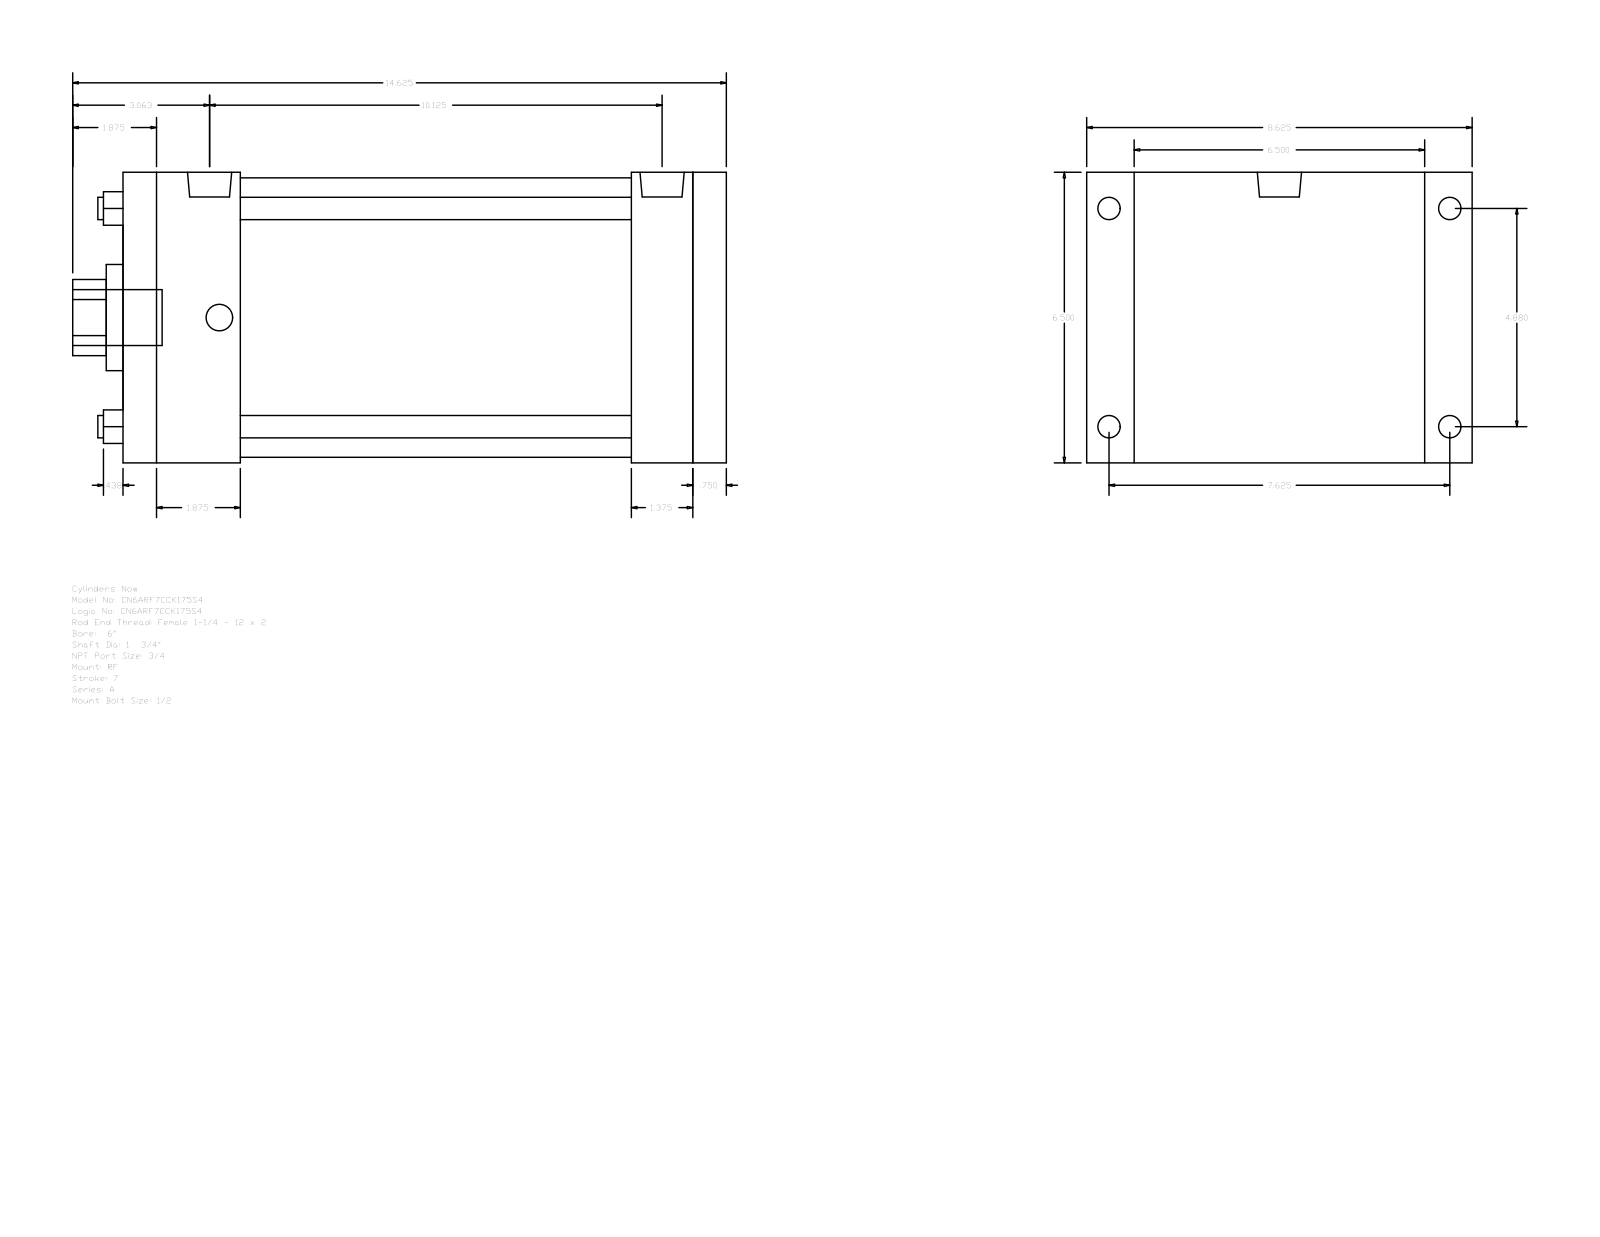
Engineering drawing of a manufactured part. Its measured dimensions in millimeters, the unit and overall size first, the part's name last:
Units: millimetres
Overall size (bounding box): 371.48 × 219.07 × 165.1
Round holes (diameter × count): ⌀12.7 ×4, ⌀44.45 ×1, ⌀60.33 ×1, ⌀158.75 ×1
Round bosses / shafts (diameter × count): ⌀15.08 ×4, ⌀12.7 ×4, ⌀25.12 ×2, ⌀31.75 ×1
Partial cylindrical surfaces — rounded edges, fillets, slot ends (radius × count): R21.63 ×1
Main face-to-face distances: 165.1, 342.91, 19.05, 323.86, 66.68, 257.18, 276.23, 288.93, 222.25, 34.93
Hole centre spacings: 87.65, 123.96, 175.31
Bodies: 0 solids, 92 faces (64 planar, 28 cylindrical, 0 other)
Part name (STEP PRODUCT): A_RF__0600_1.75
STEP written by: GSSL Pune (CONFIG_CONTROL_DESIGN)
